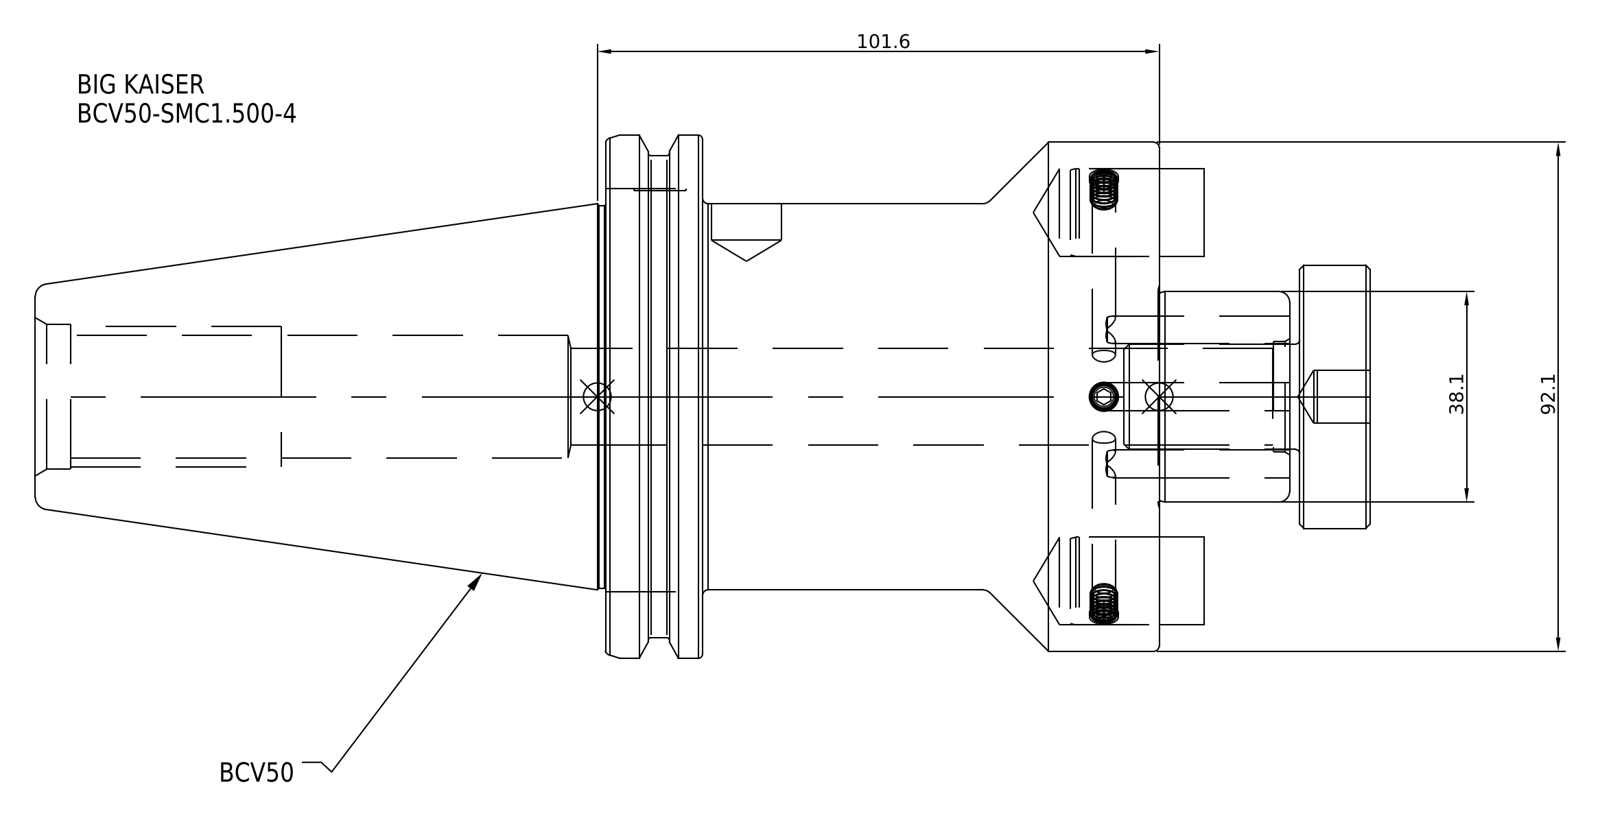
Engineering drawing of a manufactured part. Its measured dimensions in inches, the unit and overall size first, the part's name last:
Units: inches
Overall size (bounding box): 8.318 × 3.875 × 3.875
Round holes (diameter × count): ⌀0.687 ×1
Round bosses / shafts (diameter × count): ⌀3.875 ×1, ⌀3.626 ×1, ⌀3.594 ×1, ⌀2.75 ×1
Main face-to-face distances: 3.941, 3.25, 0.691, 8, 4.75, 4.059, 0.625, 0.318, 3.568, 4.259
Volume: 46.22 in³ · Surface area: 102.4 in²
Bodies: 1 solid, 39 faces (17 planar, 14 cylindrical, 8 other)
Part name (STEP PRODUCT): BCV50-SMC1_500-4
STEP written by: SolidWorks 2021 (CONFIG_CONTROL_DESIGN)
